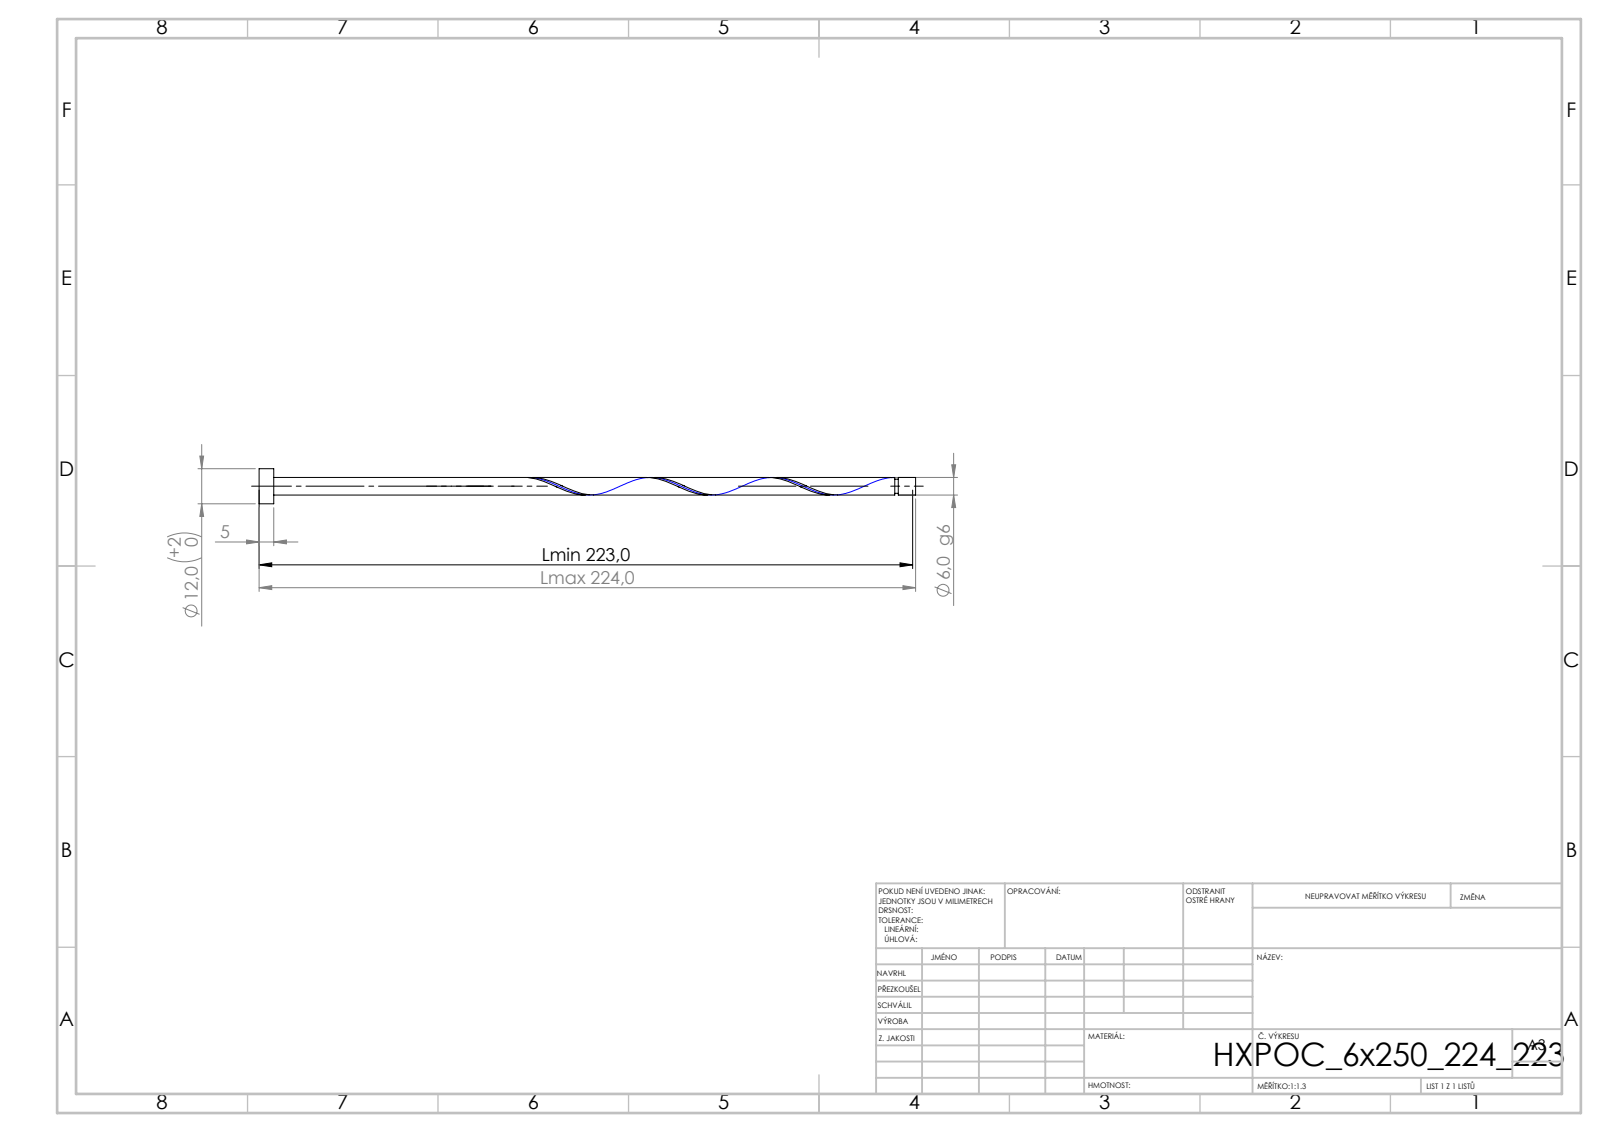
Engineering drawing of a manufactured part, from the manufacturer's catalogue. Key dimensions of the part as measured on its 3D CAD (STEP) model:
STEP written by: SolidWorks 2019 (CONFIG_CONTROL_DESIGN)
Units: millimetres
Bodies: 1 solid, 21 faces (6 planar, 14 cylindrical, 1 other)
Overall size (bounding box): 224 × 12 × 12
Volume: 6 678 mm³ · Surface area: 4 639 mm²
Round bosses / shafts (diameter × count): ⌀12 ×1, ⌀6 ×1, ⌀4.8 ×1
Main face-to-face distances: 5, 224, 219, 218.09, 213.09, 5.91, 216.89, 211.89, 1.2, 7.11
